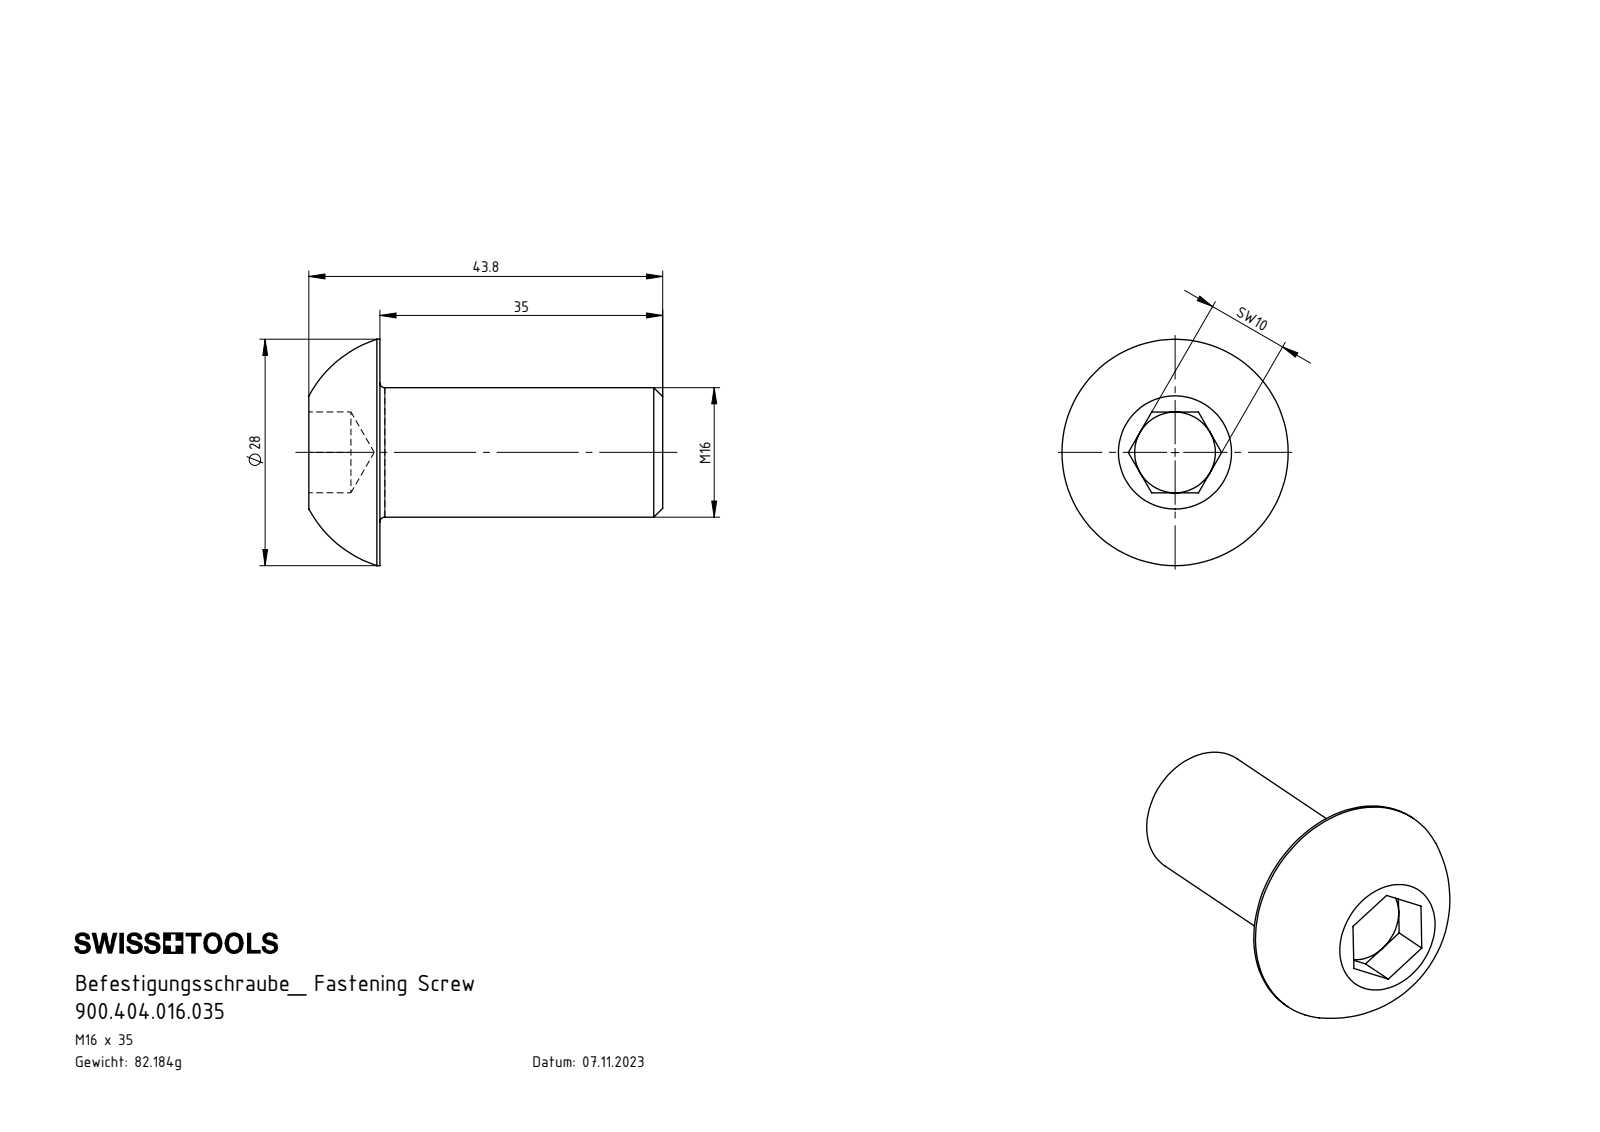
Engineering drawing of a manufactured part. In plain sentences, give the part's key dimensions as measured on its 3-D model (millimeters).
The part is named "900.404.016.035". Its 3-D file was written by "SolidWorks 2022 (AUTOMOTIVE_DESIGN)". It is 1 solid with 27 faces: 15 planar, 4 cylindrical and 8 other. Overall it measures 43.8 by 28 by 28 millimeters. Its volume is 10 273 cubic millimeters and its surface area 3 486 square millimeters. Round bosses or shafts: 1 of diameter 28, 1 of diameter 16. The main face-to-face distances are 35, 10, 8.8, 43.8, 5.2, 3.6, 38.6.
